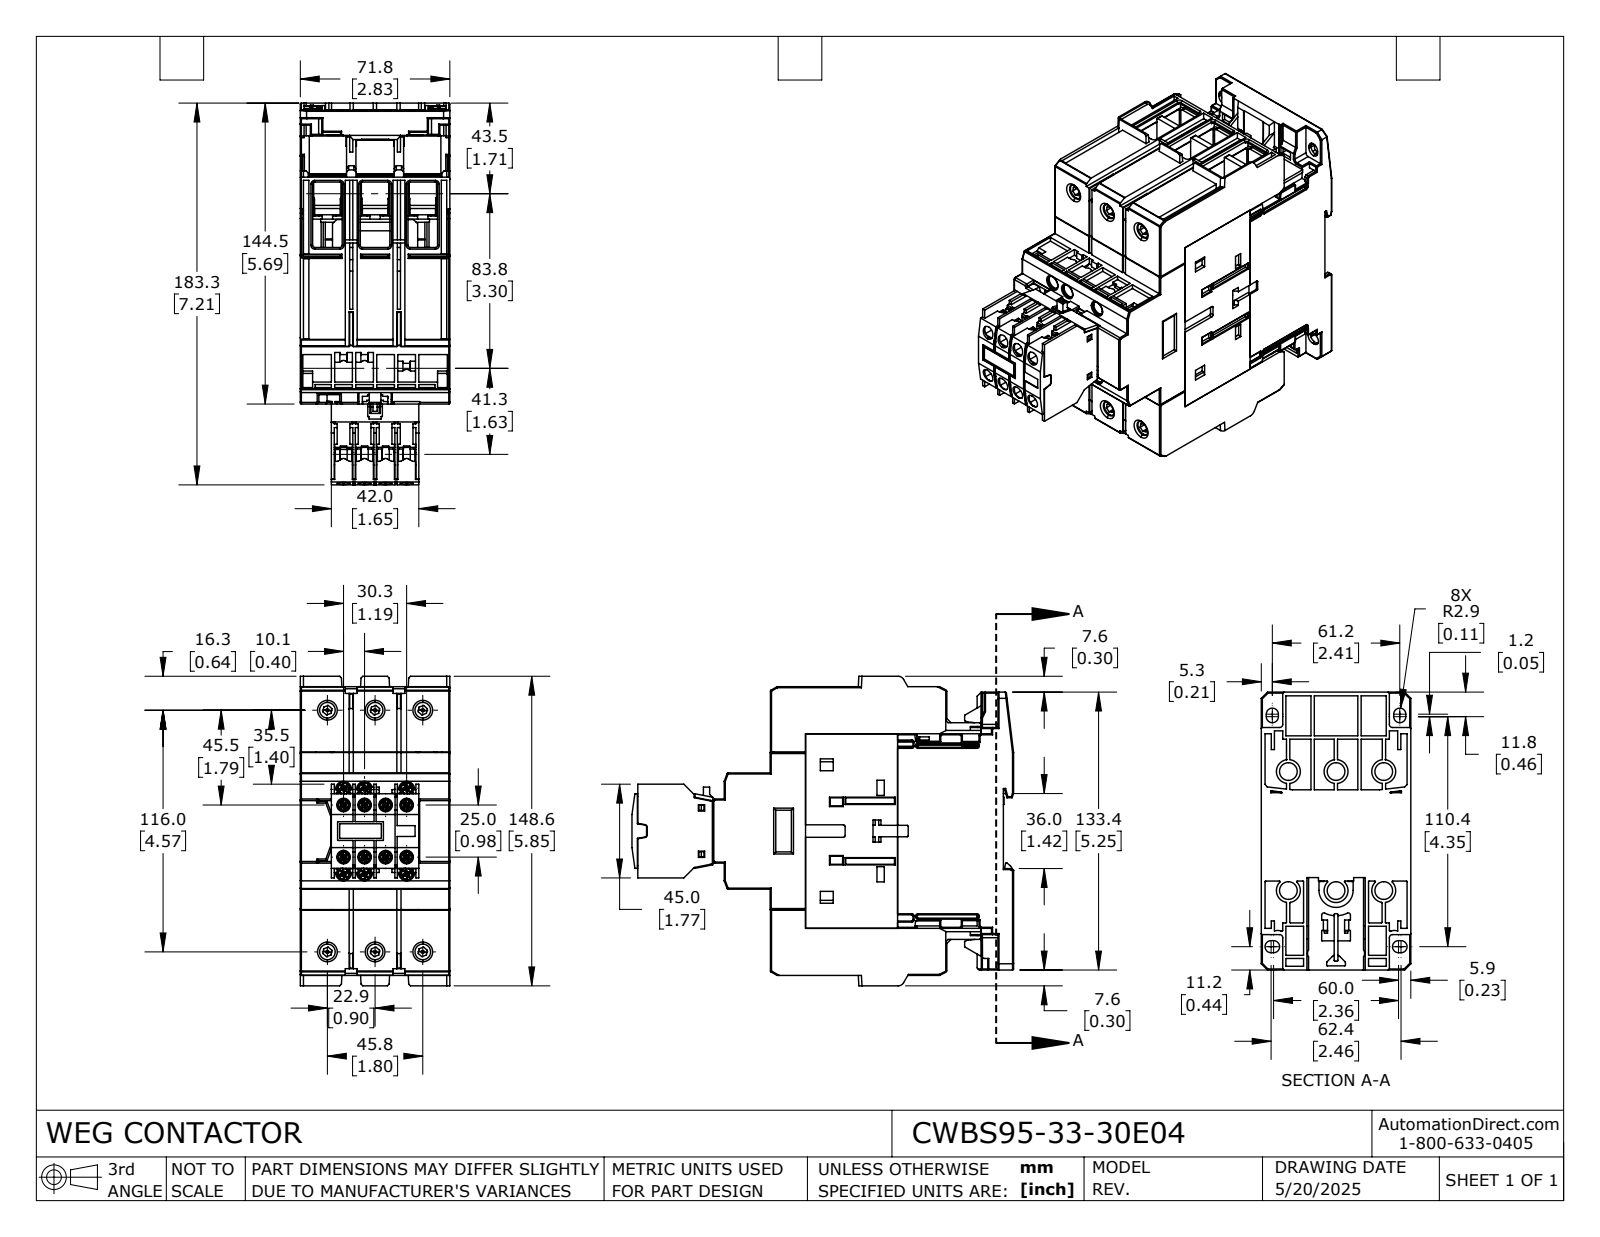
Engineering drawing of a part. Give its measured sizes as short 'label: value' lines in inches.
name: CWBS95-33-30E04
written by: SolidWorks 2024 (AUTOMOTIVE_DESIGN)
unit: in
bodies: 42 solids, 7161 faces (4791 planar, 1513 cylindrical, 857 other)
size: 7.215 × 5.85 × 2.827
volume: 54.55 in³; area: 511.4 in²
holes: 10× ⌀0.165, 8× ⌀0.13, 8× ⌀0.256, 6× ⌀0.114, 6× ⌀0.264, 6× ⌀0.276, 6× ⌀0.295, 6× ⌀0.335, 6× ⌀0.374, 4× ⌀0.287, 1× ⌀0.124
bosses: 8× ⌀0.138, 6× ⌀0.366, 6× ⌀0.313, 6× ⌀0.14, 5× ⌀0.453, 5× ⌀0.107, 3× ⌀0.107, 2× ⌀0.276
rounds: 274× R0.02, 156× R0.012, 113× R0.016, 64× R0.004, 49× R0.039, 36× R0.024, 24× R0.059, 14× R0.031
face distances: 0.059, 0.902, 2.827, 1.835, 0.874, 0.992, 0.933, 0.118, 1.776, 1.894
hole spacings: 0.902, 1.469, 3.525, 1.159, 1.535, 3.408, 0.398, 0.455
